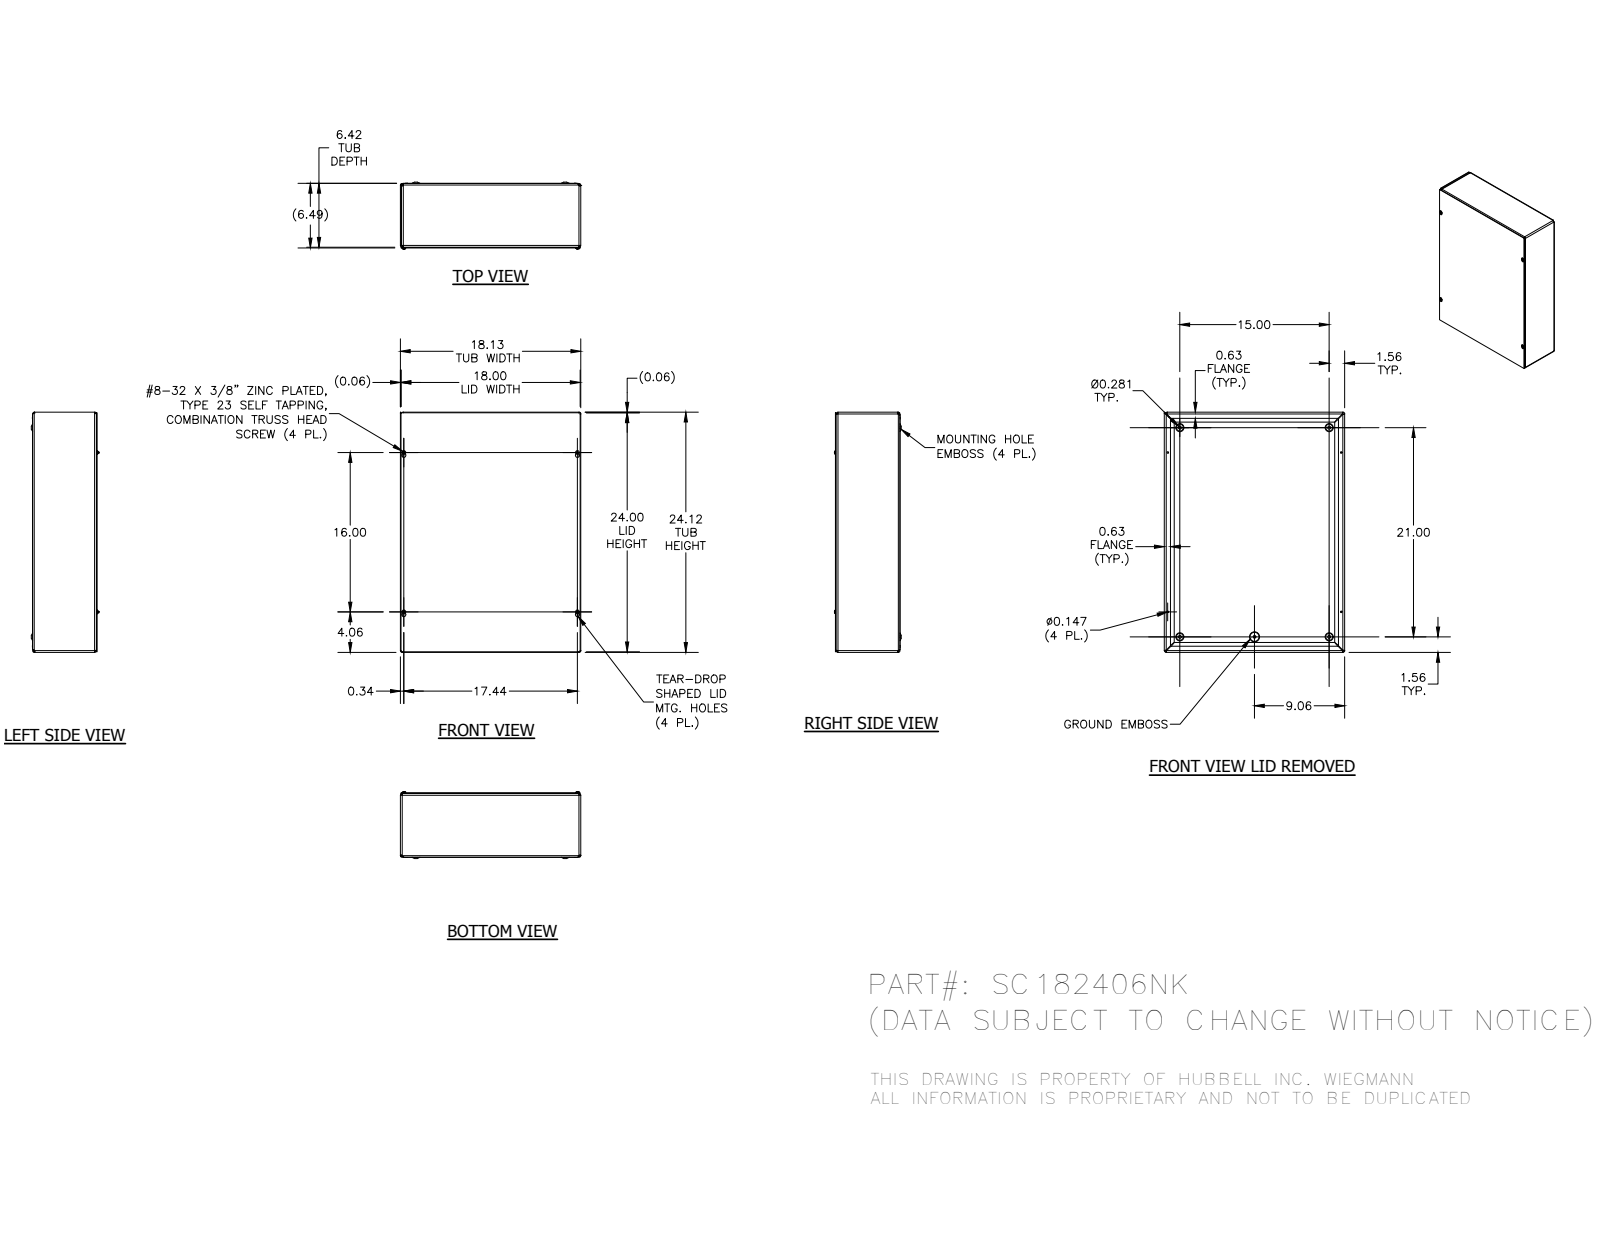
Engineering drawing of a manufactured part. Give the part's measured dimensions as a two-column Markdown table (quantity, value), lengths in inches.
| quantity | value |
| --- | --- |
| part name | SC1824BKP; SC182406NKWRA; SC1824LID; 34056 (+1 more) |
| STEP written by | Autodesk Inventor 2014 (AUTOMOTIVE_DESIGN) |
| units | inches |
| bodies | 7 solids, 358 faces (133 planar, 75 cylindrical, 150 other) |
| overall size | 24.125 × 18.125 × 6.716 |
| volume | 103.3 in³ |
| surface area | 3 032 in² |
| round holes (diameter × count) | 0.147 × 4, 0.3 × 4, 0.165 × 1 |
| round bosses / shafts (diameter × count) | 0.18 × 8, 0.384 × 4, 0.164 × 4, 0.228 × 1 |
| partial cylindrical surfaces (radius × count) | 0.125 × 12, 0.187 × 8, 0.055 × 4, 0.062 × 4, 0.094 × 4, 0.117 × 4, 0.124 × 4, 0.156 × 4 |
| main face-to-face distances | 0.074, 6.417, 6.343, 6.491, 0.062, 0.062, 18.063, 18.001, 18.125, 18.063 |
| hole center spacings | 18.54, 24.603, 2.781, 2.781, 7.5, 15, 16, 16.41 |
